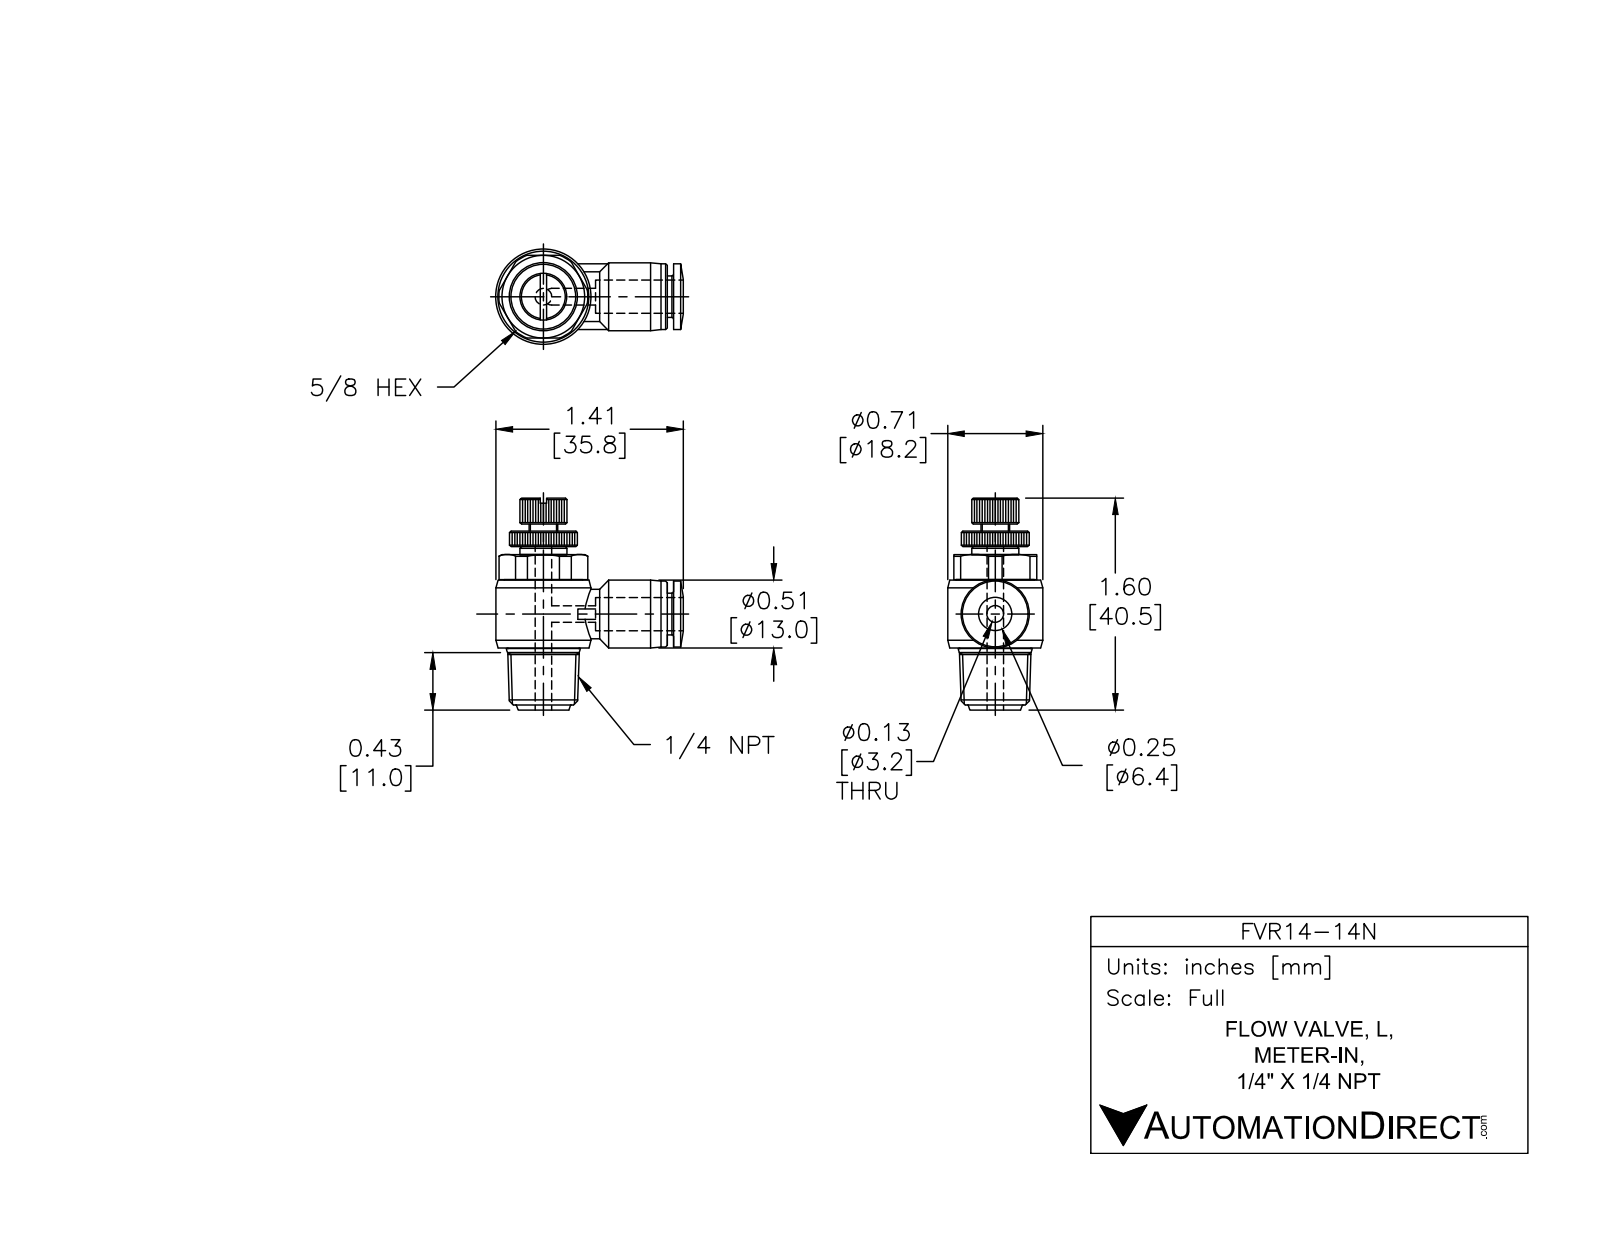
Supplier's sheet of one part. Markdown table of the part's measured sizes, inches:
| quantity | value |
| --- | --- |
| part name | FVR14-14N |
| STEP written by | SolidWorks 2015 (AUTOMOTIVE_DESIGN) |
| units | inches |
| bodies | 1 solid, 424 faces (186 planar, 112 cylindrical, 126 other) |
| overall size | 1.85 × 1.413 × 0.717 |
| volume | 0.49 in³ |
| surface area | 6.727 in² |
| round holes (diameter × count) | 0.177 × 2, 0.258 × 1 |
| round bosses / shafts (diameter × count) | 0.717 × 1, 0.591 × 1, 0.539 × 1, 0.512 × 1, 0.496 × 1, 0.374 × 1, 0.354 × 1, 0.313 × 1 |
| partial cylindrical surfaces (radius × count) | 0.256 × 1, 0.335 × 1 |
| main face-to-face distances | 0.177, 0.705, 0.882, 0.624, 0.764, 0.469, 0.047, 0.37, 0.059, 0.118 |
